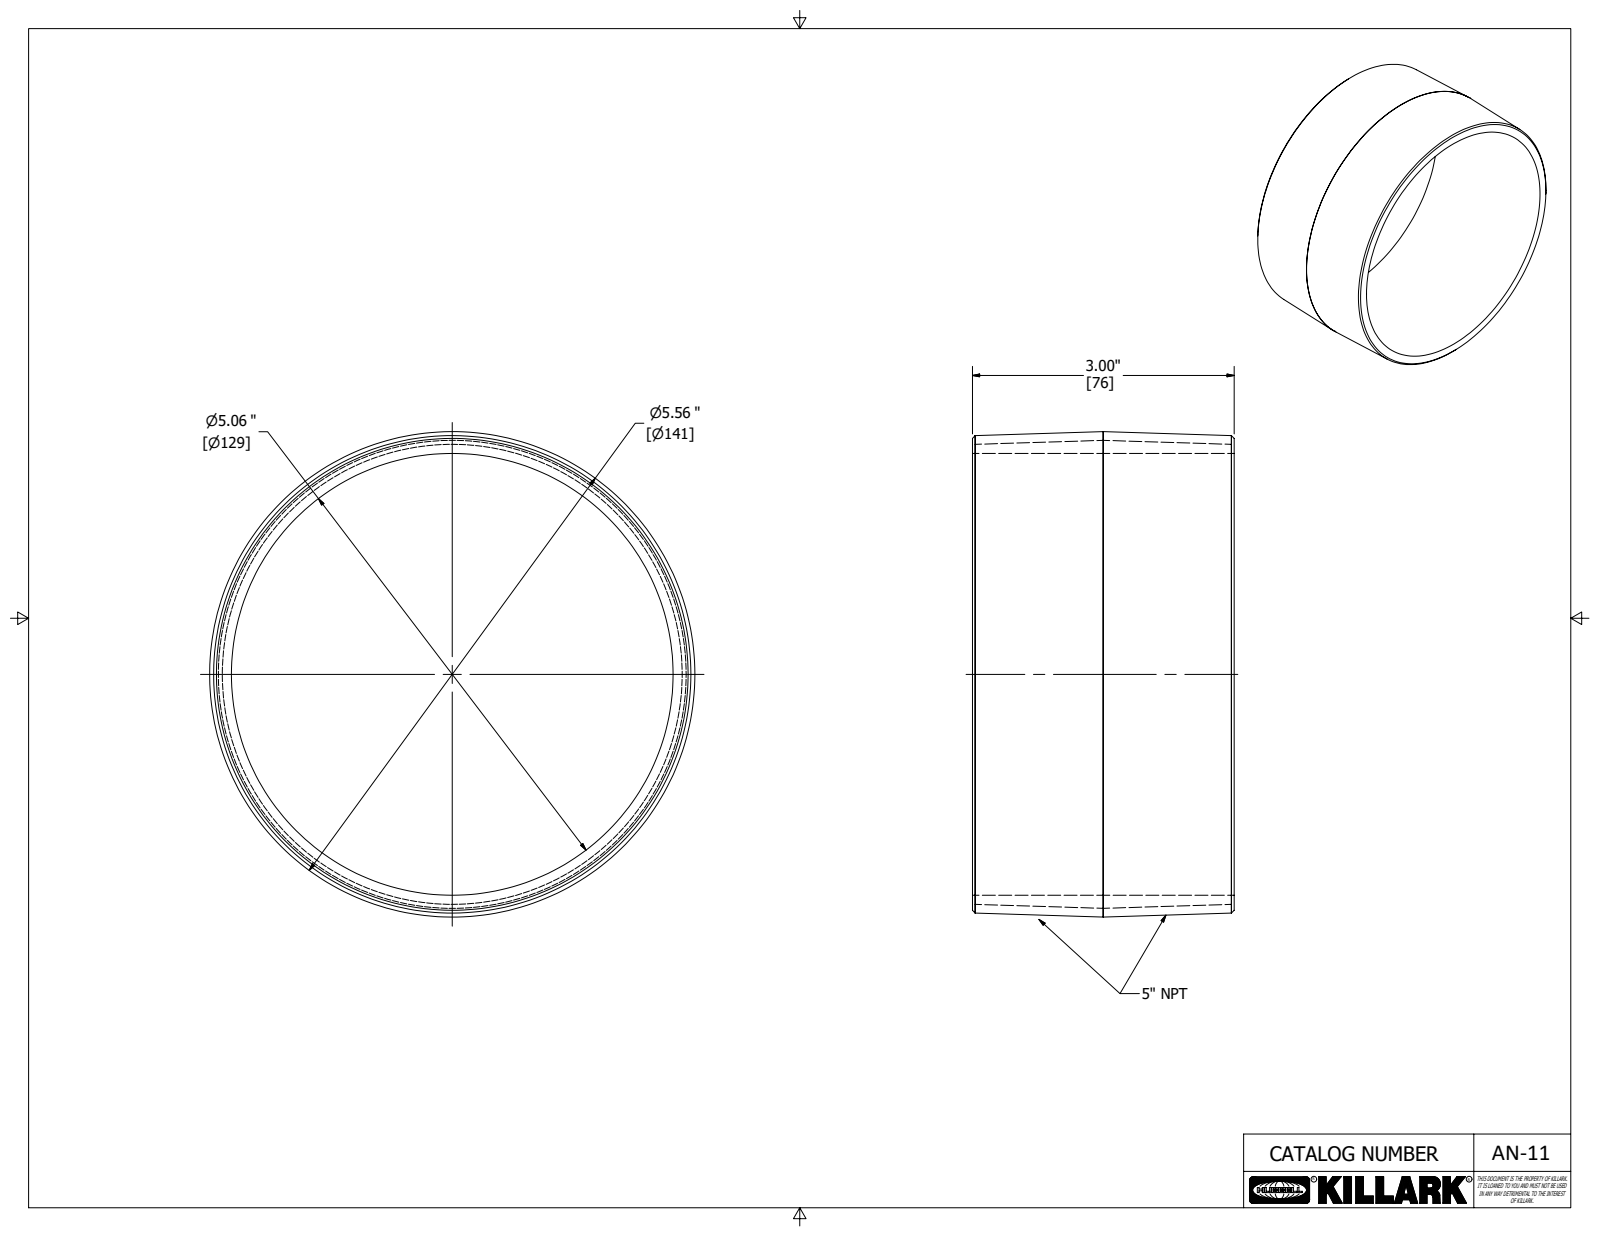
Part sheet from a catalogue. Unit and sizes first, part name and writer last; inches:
Units: inches
Overall size (bounding box): 5.562 × 5.562 × 3
Round holes (diameter × count): ⌀5.063 ×1
Round bosses / shafts (diameter × count): ⌀5.563 ×1
Main face-to-face distances: 3
Volume: 11.28 in³ · Surface area: 105.8 in²
Bodies: 1 solid, 8 faces (2 planar, 2 cylindrical, 4 other)
Part name (STEP PRODUCT): AN-11
STEP written by: Autodesk Inventor 2020 (AUTOMOTIVE_DESIGN)
